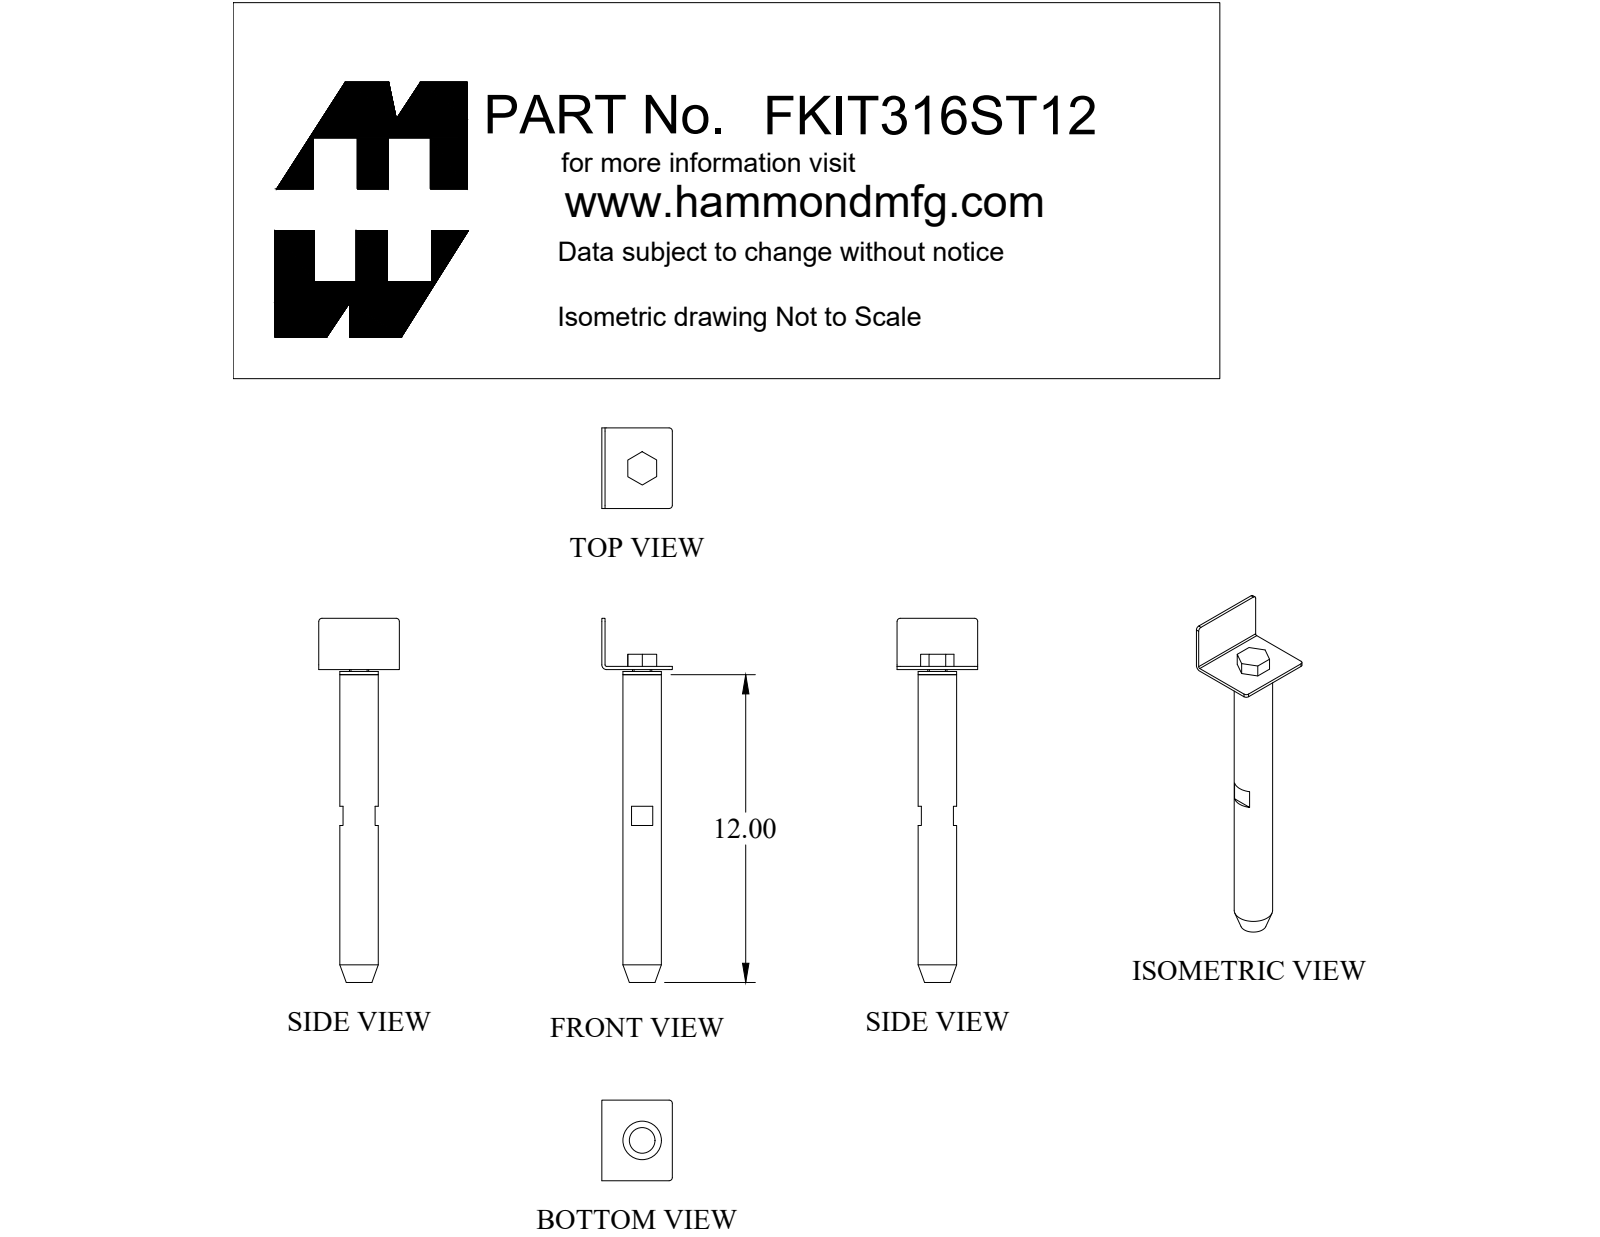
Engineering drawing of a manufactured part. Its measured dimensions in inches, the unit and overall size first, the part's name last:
Units: inches
Overall size (bounding box): 14.197 × 3.144 × 2.75
Round holes (diameter × count): ⌀0.625 ×1, ⌀0.719 ×1, ⌀0.875 ×1
Round bosses / shafts (diameter × count): ⌀1.5 ×1, ⌀0.75 ×1
Partial cylindrical surfaces — rounded edges, fillets, slot ends (radius × count): R0.125 ×4, R0.06 ×1, R0.185 ×1
Main face-to-face distances: 0.125, 0.197, 0.322, 0.125, 0.072, 0.197, 0.796, 0.671, 0.599, 0.474
Volume: 23.24 in³ · Surface area: 110.3 in²
Bodies: 4 solids, 42 faces (27 planar, 12 cylindrical, 3 other)
Part name (STEP PRODUCT): FKIT316ST12
STEP written by: SolidWorks 2019 (CONFIG_CONTROL_DESIGN)
